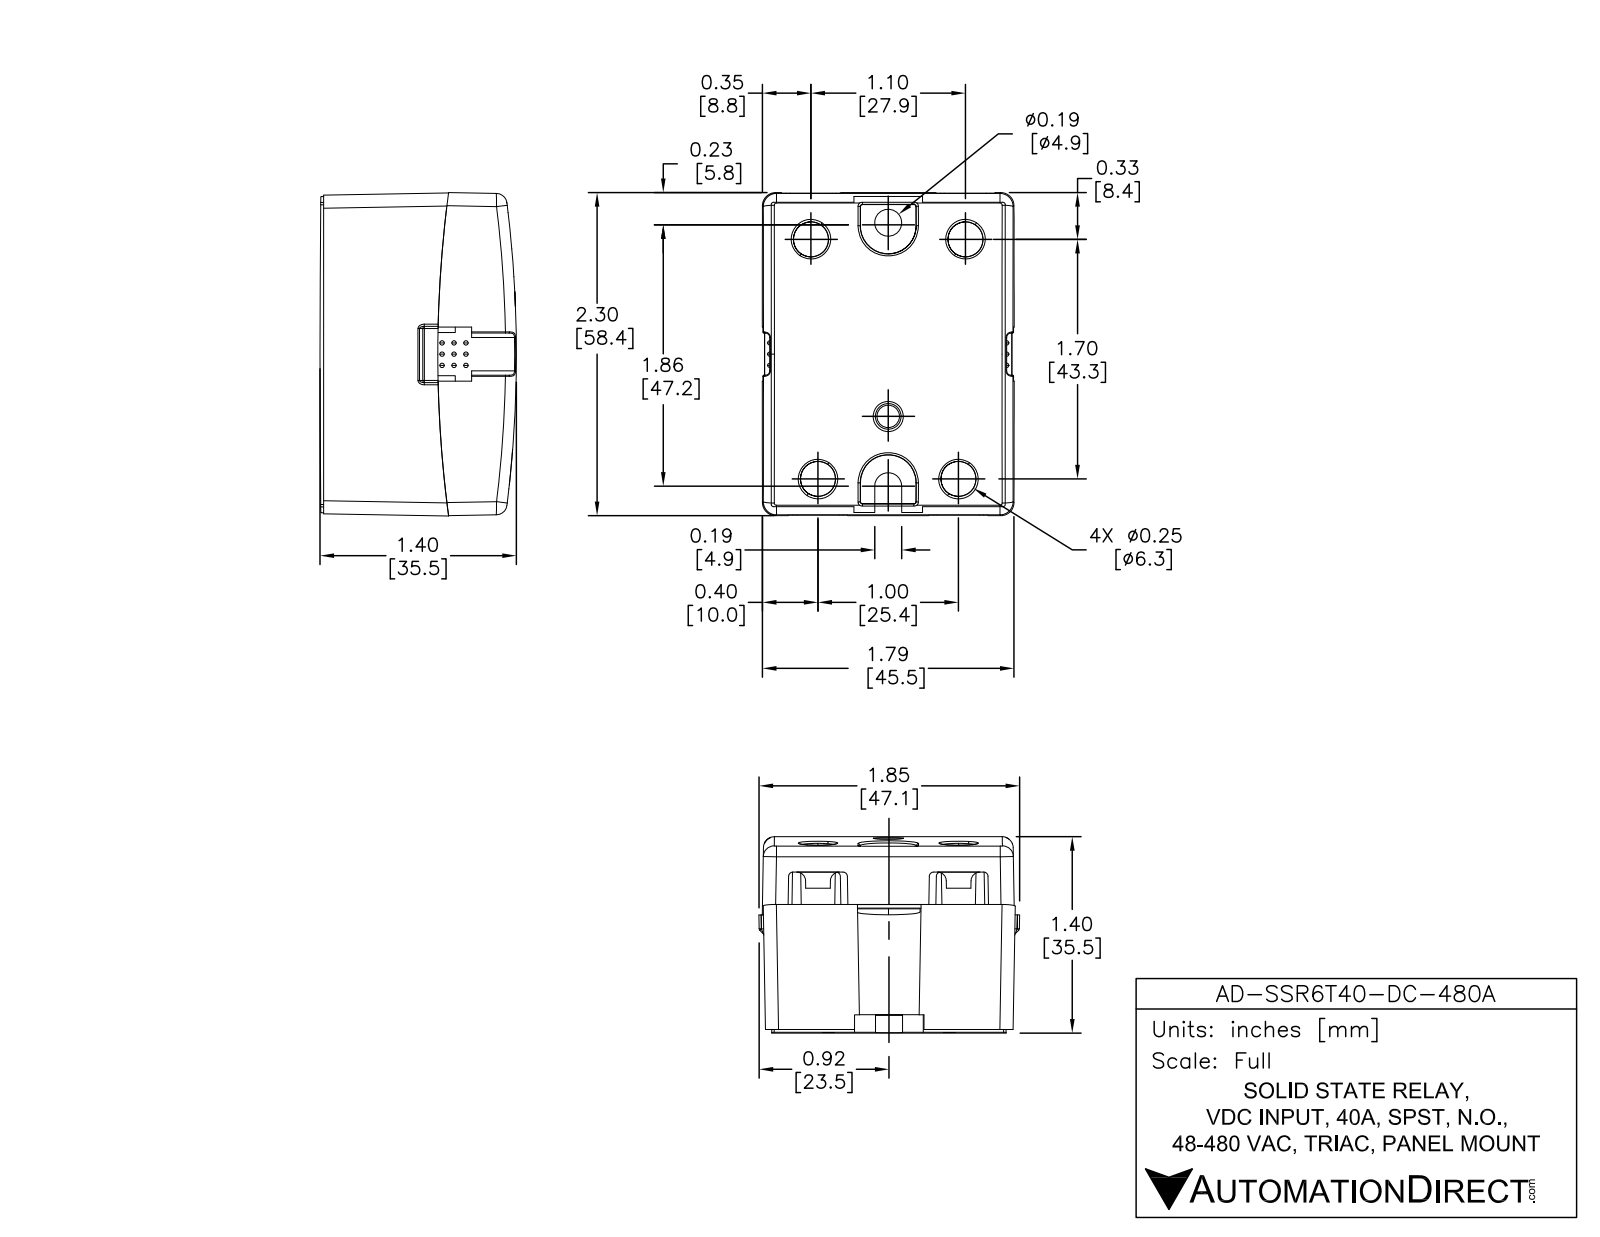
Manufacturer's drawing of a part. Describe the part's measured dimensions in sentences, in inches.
The part is named "AD-SSR6T40-DC-480A". Its 3-D file was written by "SolidWorks 2013 (AUTOMOTIVE_DESIGN)". It is 3 solids with 251 faces: 145 planar, 95 cylindrical and 11 other. Overall it measures 2.3 by 1.79 by 1.4 inches. Its volume is 5.14 cubic inches and its surface area 26.41 square inches. Round holes: 4 of diameter 0.25, 1 of diameter 0.19. Round bosses or shafts: 2 of diameter 0.4, 2 of diameter 0.35, 2 of diameter 0.3, 2 of diameter 0.25, 2 of diameter 0.2, 2 of diameter 0.2. Partial cylindrical surfaces (rounded edges, fillets, slot ends): 6 of radius 0.03, 4 of radius 0.01, 4 of radius 0.04, 4 of radius 0.5, 2 of radius 0.194, 1 of radius 0.095, 1 of radius 0.5, 1 of radius 0.5. The main face-to-face distances are 1.79, 2.3, 1.166, 0.25, 0.916, 0.671, 1.059, 0.5, 1.8, 0.08. The hole center spacings are 0.556, 0.565, 1, 1.1, 1.7, 1.701, 1.876, 1.879.
